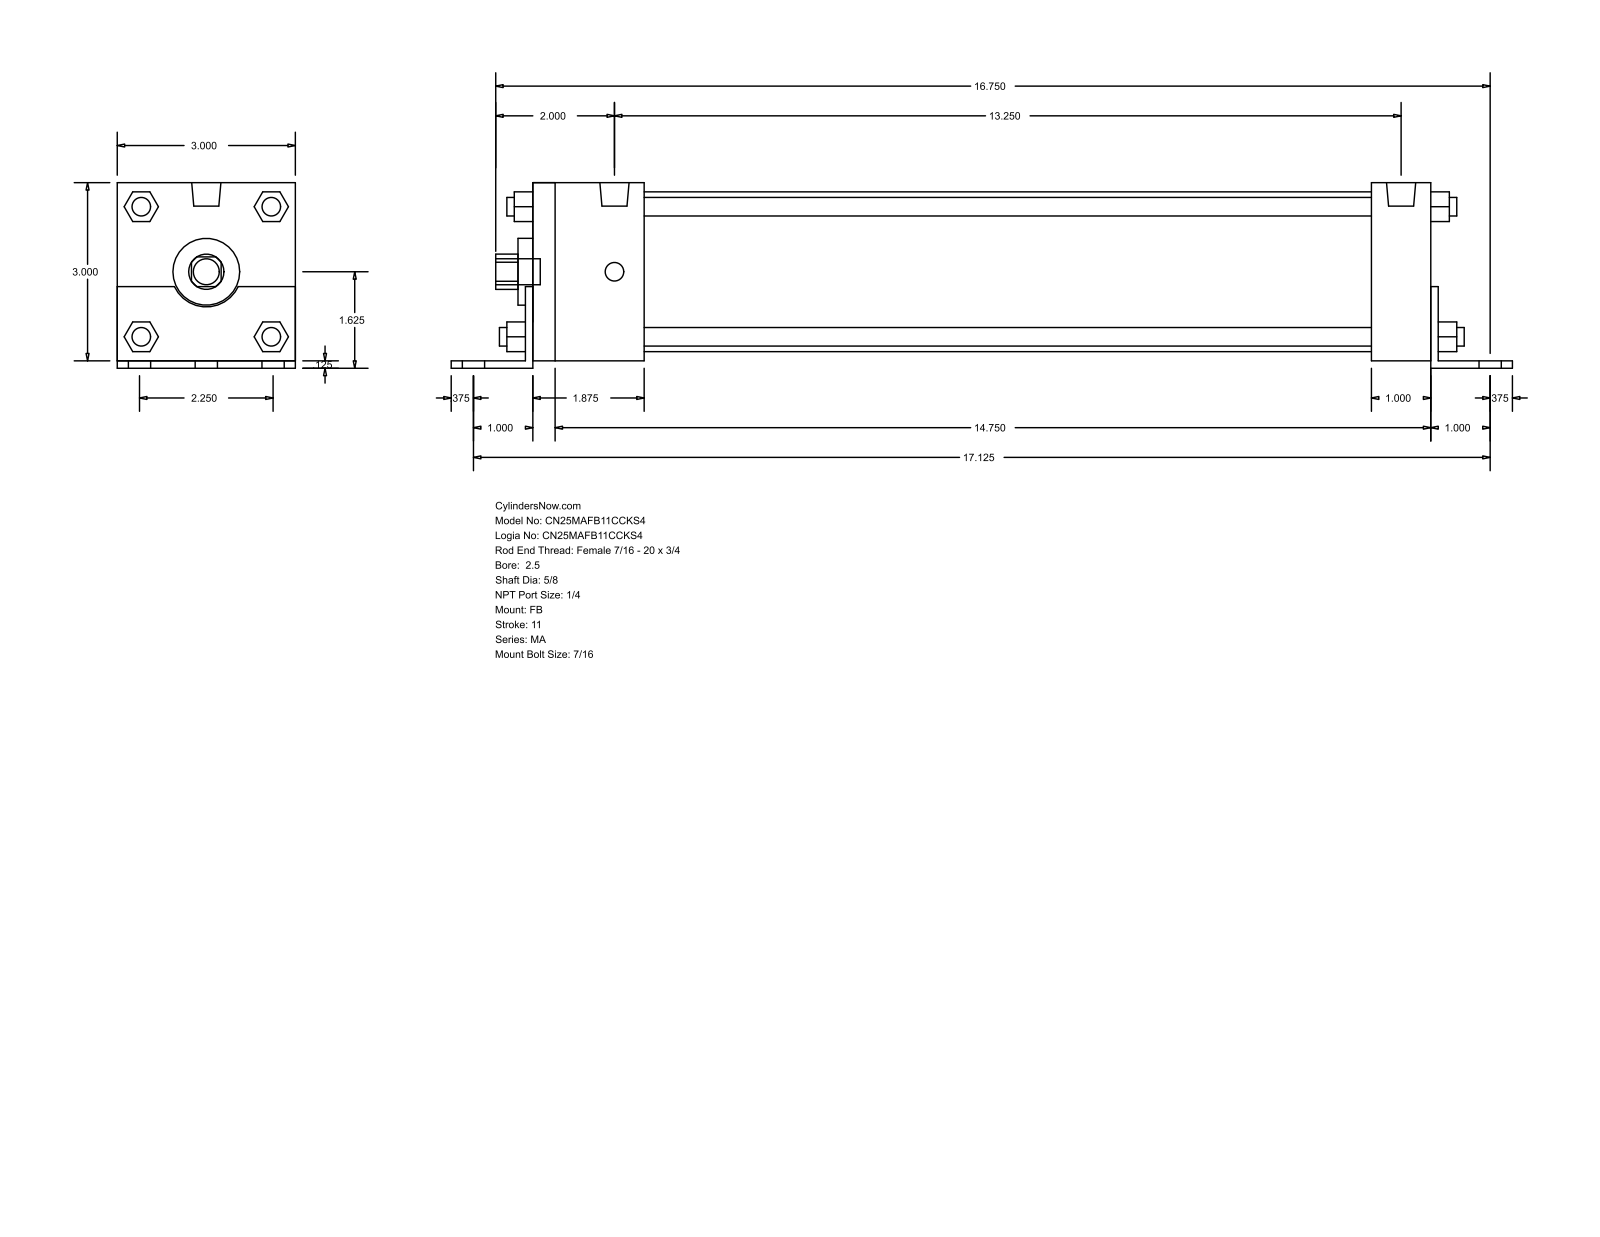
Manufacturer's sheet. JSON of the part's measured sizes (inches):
{"part_name": "MA_FB__0250_0.625", "step_written_by": "GSSL Pune (CONFIG_CONTROL_DESIGN)", "units": "inches", "bodies": {"solids": 0, "faces": 140, "planar": 105, "cylindrical": 35, "other": 0}, "overall_size": [17.875, 3.125, 3], "round_holes": [[0.625, 1], [1.125, 1], [2.69, 1]], "round_bosses_or_shafts": [[0.313, 8], [0.437, 7], [0.492, 2]], "partial_cylinders_radius": [[0.297, 1], [0.593, 1]], "face_to_face_distances": [3, 0.125, 3.125, 0.125, 15.25, 15.125, 1.125, 1.875, 1, 15.375]}
